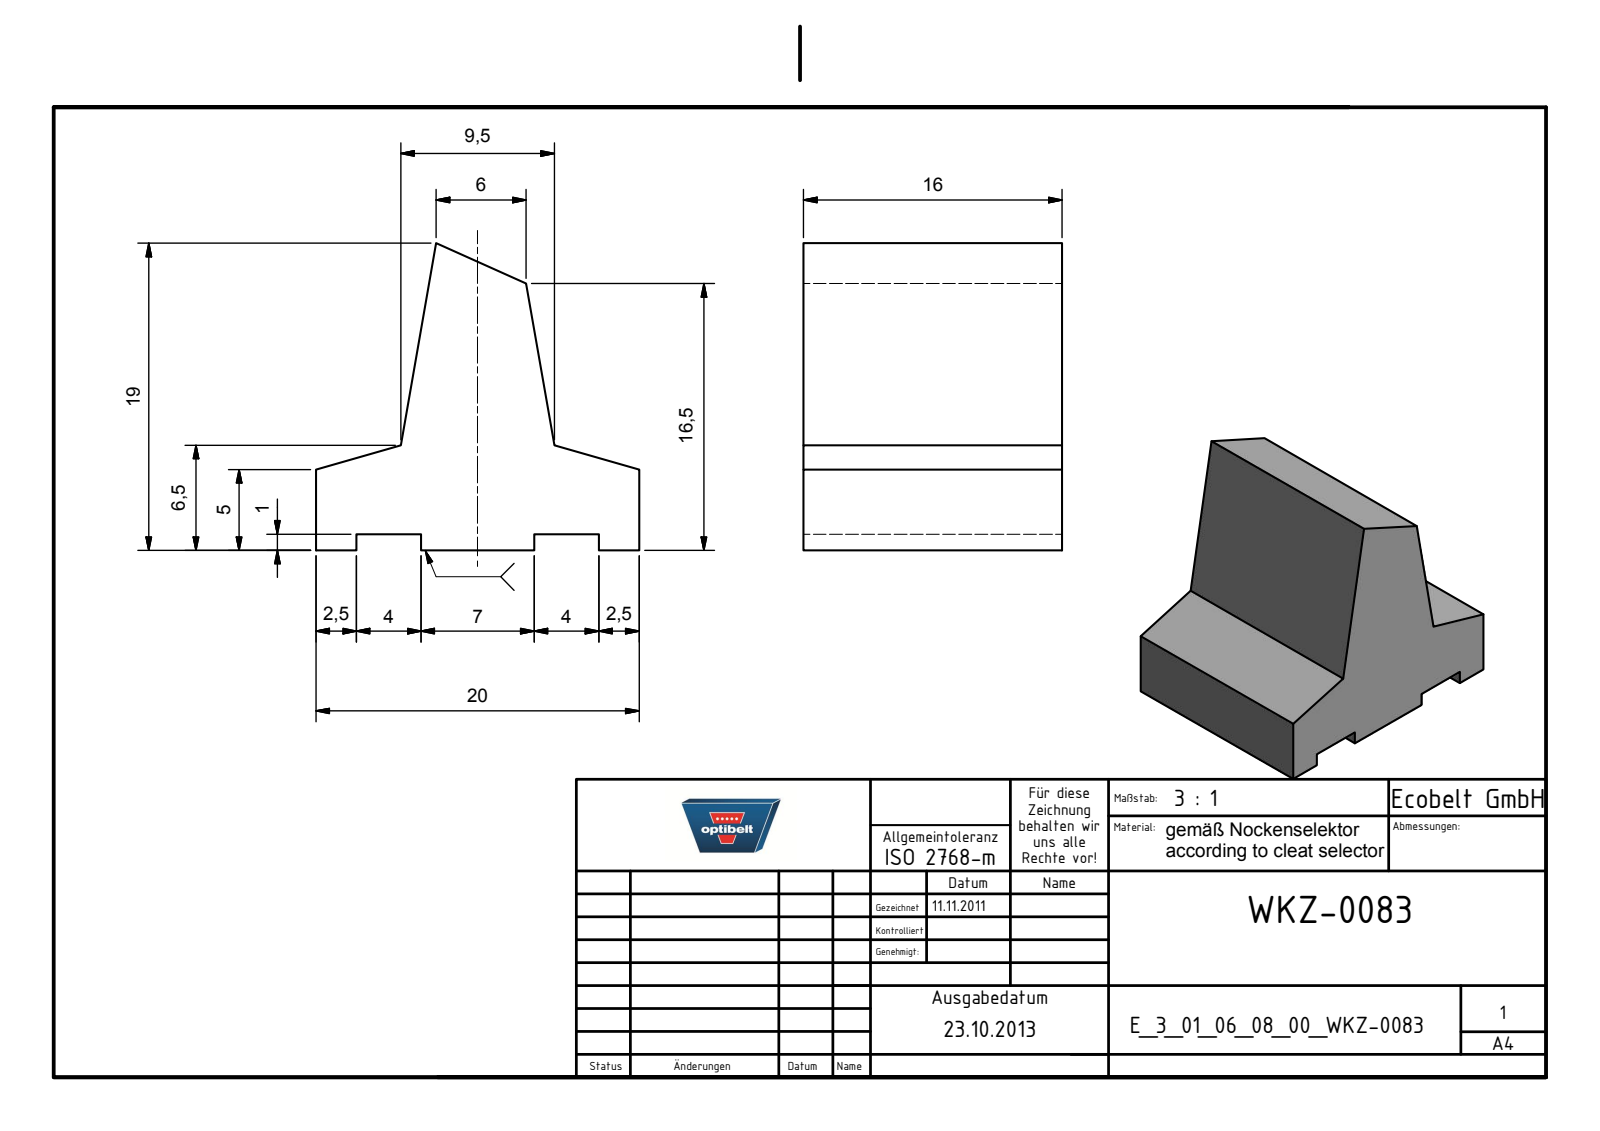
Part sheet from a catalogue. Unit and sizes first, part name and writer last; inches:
Units: inches
Overall size (bounding box): 0.787 × 0.748 × 0.63
Main face-to-face distances: 0.63, 0.039, 0.787, 0.098, 0.256, 0.531, 0.689, 0.157, 0.433, 0.591
Volume: 0.194 in³ · Surface area: 2.449 in²
Bodies: 1 solid, 18 faces (18 planar, 0 cylindrical, 0 other)
Part name (STEP PRODUCT): E_3_01_06_08_00_WKZ-0083
STEP written by: Autodesk Inventor 2025 (AUTOMOTIVE_DESIGN)
